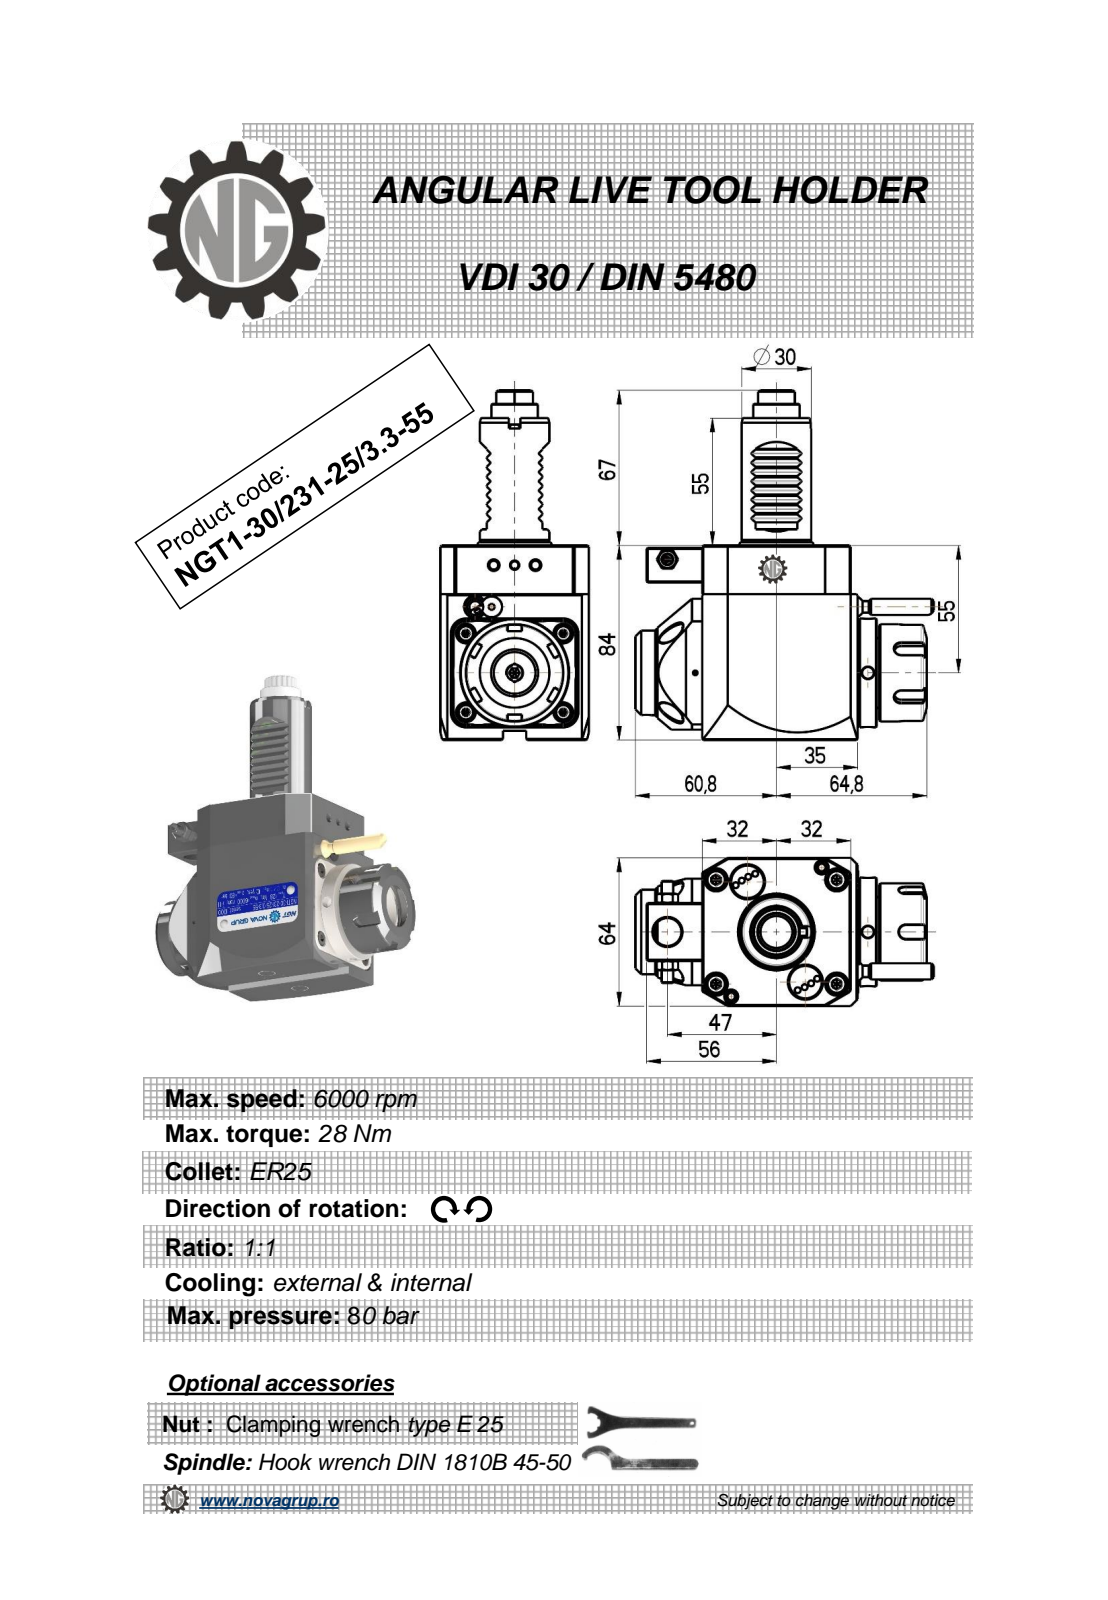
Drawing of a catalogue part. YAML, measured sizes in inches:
part_name: "NGT1_30_231_25_3_3_55"
step_written_by: "PRO/ENGINEER BY PARAMETRIC TECHNOLOGY CORPORATION, 2010280 (CONFIG_CONTROL_DESIGN)"
units: inches
bodies: {solids: 1, faces: 557, planar: 224, cylindrical: 163, other: 170}
overall_size: [5.945, 5.064, 2.52]
volume: 29.21
surface_area: 77.35
round_holes:
  - {diameter: 0.197, count: 2}
  - {diameter: 0.098, count: 1}
  - {diameter: 0.118, count: 1}
  - {diameter: 0.165, count: 1}
  - {diameter: 0.374, count: 1}
  - {diameter: 0.472, count: 1}
  - {diameter: 0.799, count: 1}
round_bosses_or_shafts:
  - {diameter: 0.353, count: 2}
  - {diameter: 0.197, count: 2}
  - {diameter: 1.85, count: 1}
  - {diameter: 1.654, count: 1}
  - {diameter: 1.437, count: 1}
  - {diameter: 1.378, count: 1}
  - {diameter: 1.181, count: 1}
  - {diameter: 0.787, count: 1}
partial_cylinders:
  - {radius: 0.078, count: 36}
  - {radius: 0.012, count: 16}
  - {radius: 0.01, count: 12}
  - {radius: 0.118, count: 5}
  - {radius: 6.299, count: 2}
  - {radius: 0.279, count: 1}
  - {radius: 0.312, count: 1}
  - {radius: 0.512, count: 1}
face_to_face_distances: [2.52, 3.307, 0.02, 2.646, 2.638, 0.295, 0.118, 0.126, 0.111, 0.315]
hole_center_spacings: [0.975, 1.307, 1.831, 3.404, 3.912]
